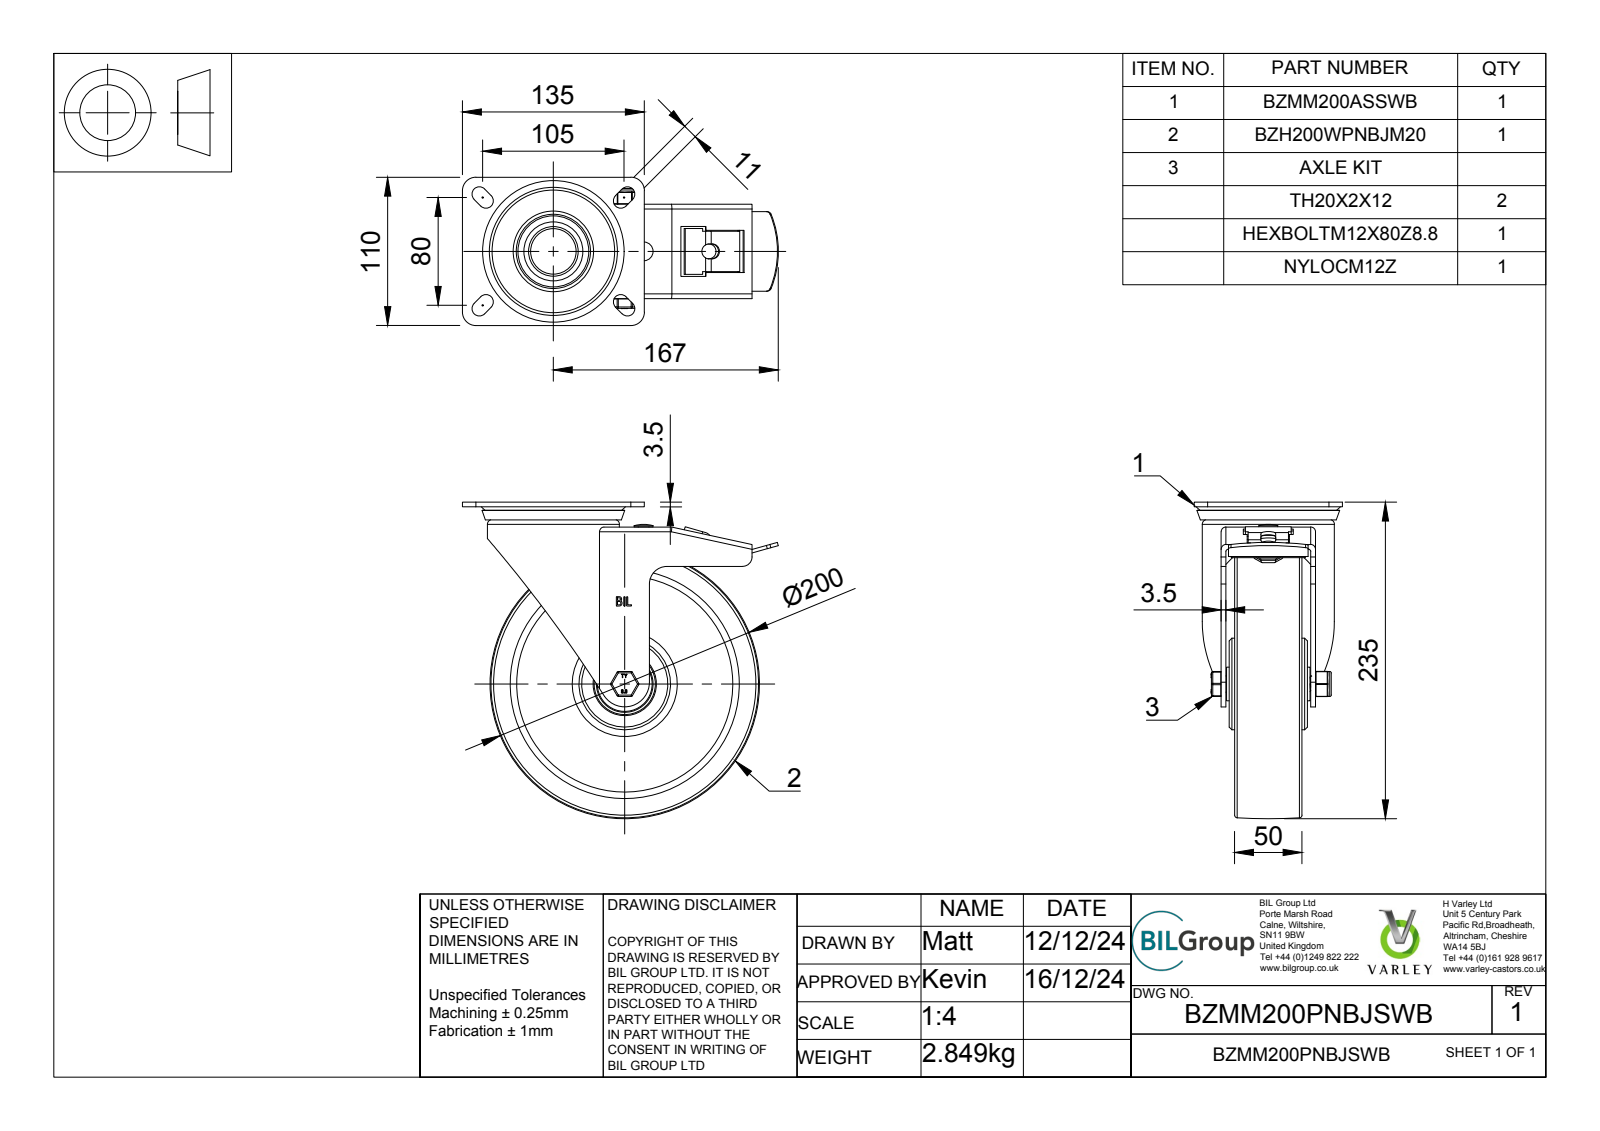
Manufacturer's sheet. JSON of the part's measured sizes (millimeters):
{"part_name": "BZMM200PNBJSWB v3; BZH200WPNBJM20 v1; BZH200WPNBJ; POLYURETHANE TYRE (+8 more)", "step_written_by": "Autodesk Translation Framework v13.20.0.188 (AP242_MANAGED_MODEL_BASED_3D_ENGINEERING_MIM_LF)", "units": "millimeters", "bodies": {"solids": 82, "faces": 1270, "planar": 538, "cylindrical": 244, "other": 488}, "overall_size": [235, 234.5, 110], "volume_mm3": 1046000, "surface_area_mm2": 382345, "round_holes": [[8, 1], [11, 1], [12, 1], [12.2, 1], [14, 1], [20, 1], [21.5, 1], [28.5, 1], [30.8, 1], [33.75, 1], [40.3, 1], [40.5, 1]], "round_bosses_or_shafts": [[98, 1], [78, 1], [68, 1], [50, 1], [40.8, 1], [39.75, 1], [31.3, 1], [27, 1]], "partial_cylinders_radius": [[0.5, 18], [1, 12], [5.5, 10], [1.75, 7], [0.25, 6], [2.5, 6], [3.5, 4], [10, 4]], "face_to_face_distances": [3.5, 13, 9.5, 6.5, 10, 3, 11.5, 30.75, 4, 19.25], "hole_center_spacings": [67]}
